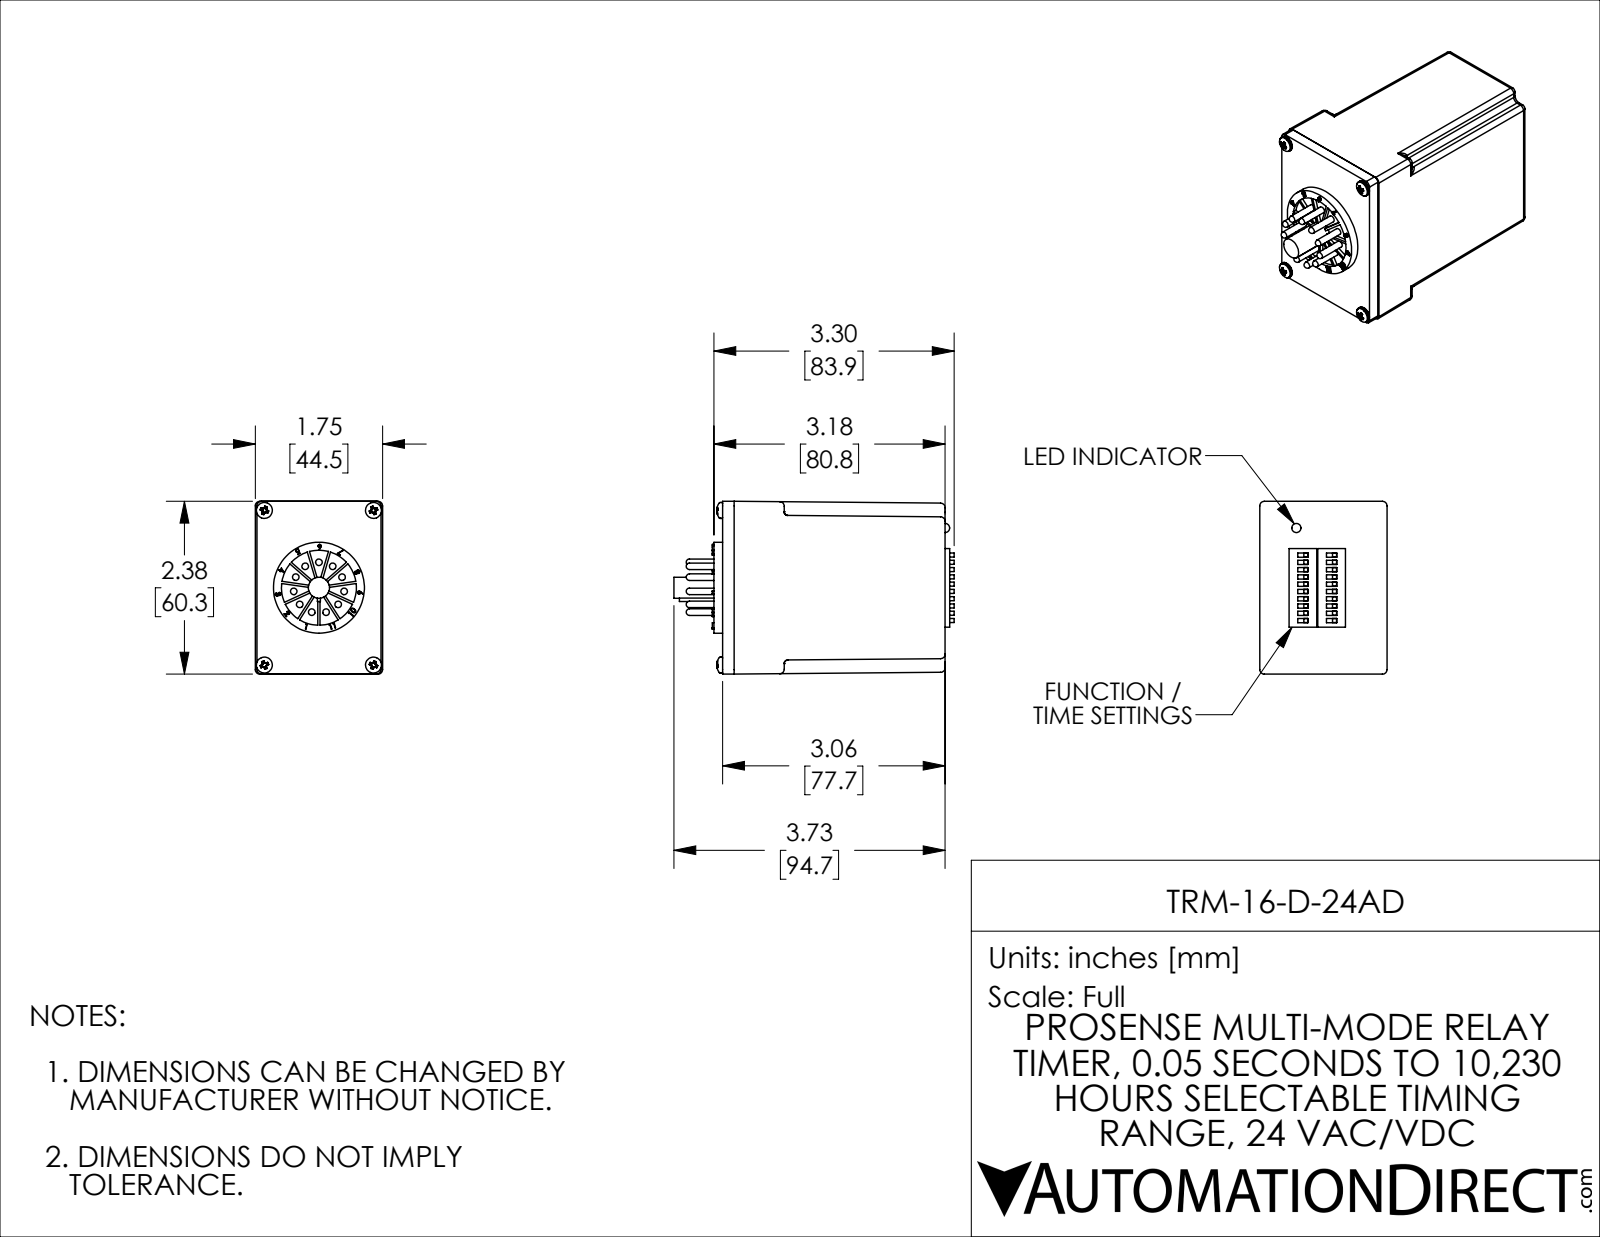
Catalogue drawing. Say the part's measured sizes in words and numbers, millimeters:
The part is named "TRM-16-D-24AD". Its 3-D file was written by "SolidWorks 2021 (CONFIG_CONTROL_DESIGN)". It is 41 solids with 800 faces: 463 planar, 158 cylindrical and 179 other. Overall it measures 97.9 by 60.3 by 44.5 millimeters. Its volume is 201 600 cubic millimeters and its surface area 31 800 square millimeters. Round holes: 4 of diameter 3.2, 1 of diameter 26.2. Round bosses or shafts: 11 of diameter 2.3, 4 of diameter 5.6, 1 of diameter 31.8, 1 of diameter 7.4. Partial cylindrical surfaces (rounded edges, fillets, slot ends): 32 of radius 1.6, 4 of radius 1.3. The main face-to-face distances are 4.1, 77.7, 73.7, 81.1, 1.3, 1.8, 5.8, 79.5, 1.6, 79.3. The hole center spacings are 33, 38.1, 54, 66.1.
